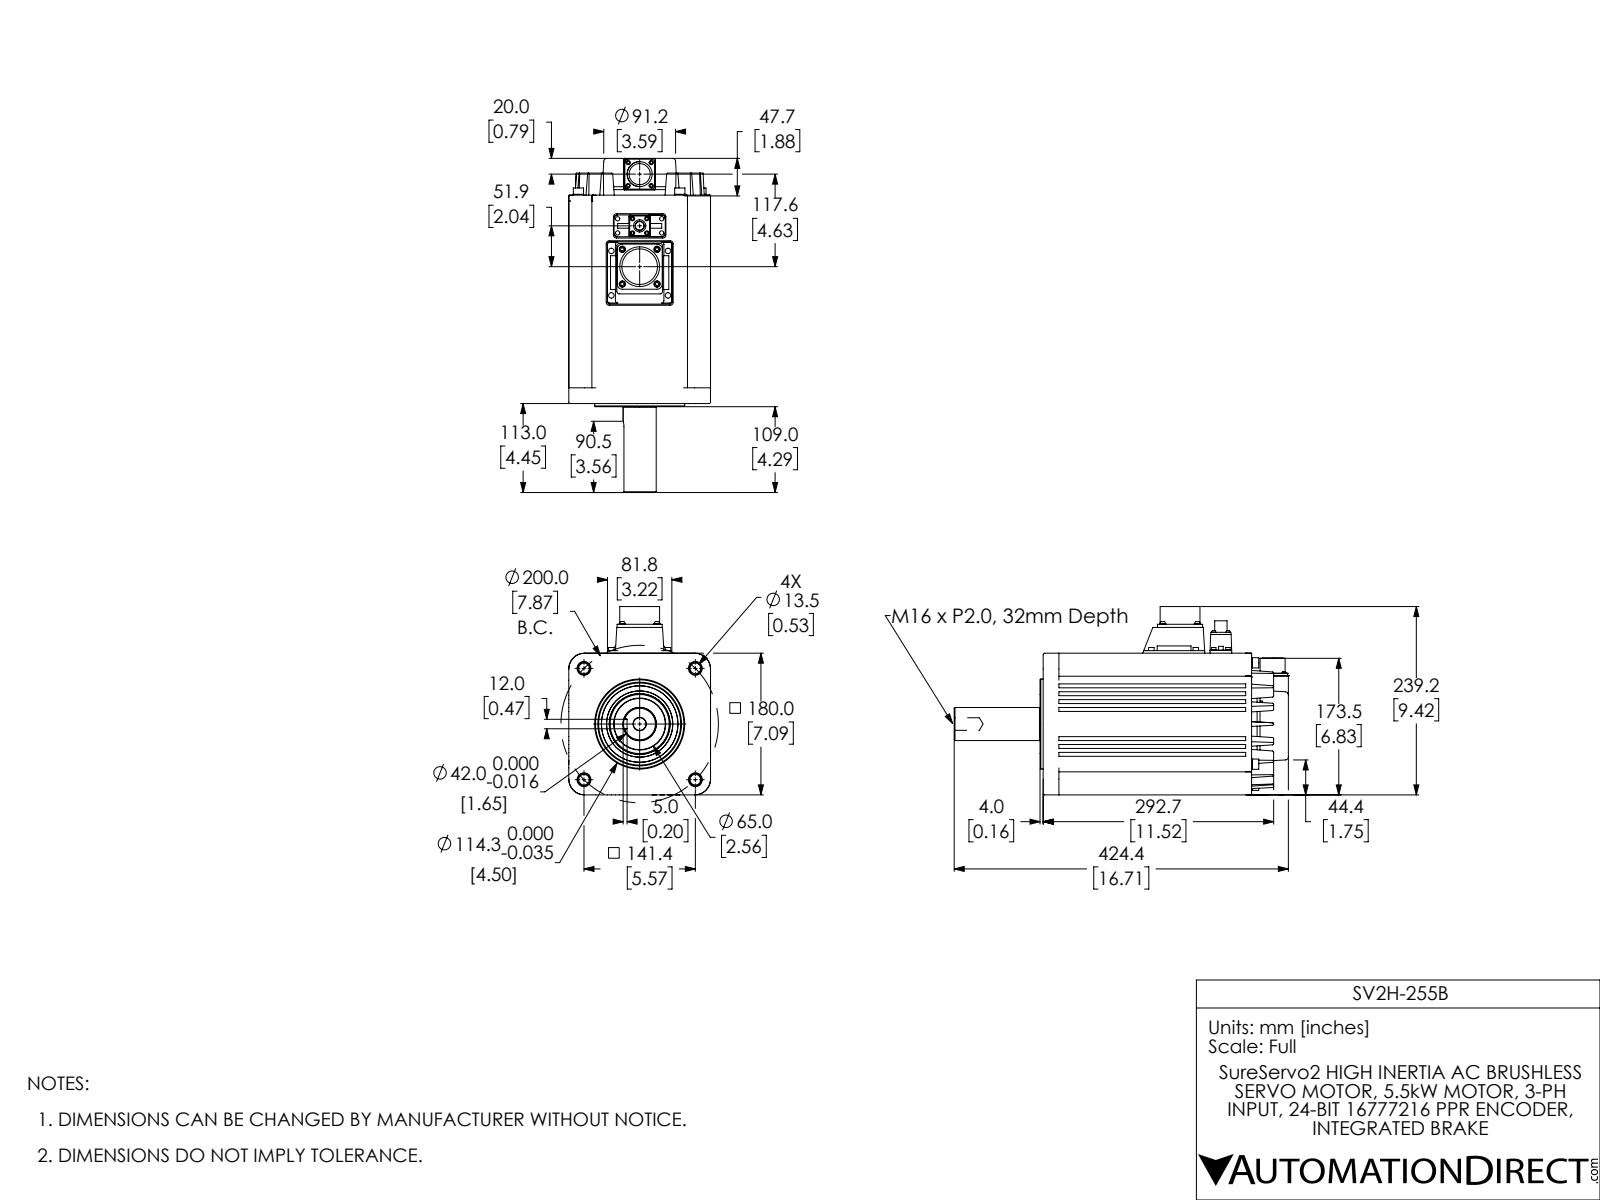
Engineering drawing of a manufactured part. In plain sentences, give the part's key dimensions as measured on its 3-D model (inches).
The part is named "SV2H-255B". Its 3-D file was written by "SolidWorks 2017 (AUTOMOTIVE_DESIGN)". It is 1 solid with 661 faces: 339 planar, 217 cylindrical and 105 other. Overall it measures 16.709 by 9.417 by 7.087 inches. Its volume is 509.7 cubic inches and its surface area 623.5 square inches. Round holes: 2 of diameter 0.315, 1 of diameter 0.461, 1 of diameter 0.63, 1 of diameter 1.058, 1 of diameter 1.783, 1 of diameter 2.559. Round bosses or shafts: 7 of diameter 0.217, 4 of diameter 0.528, 4 of diameter 0.512, 4 of diameter 0.315, 4 of diameter 0.276, 4 of diameter 0.236, 1 of diameter 4.567, 1 of diameter 4.5. Partial cylindrical surfaces (rounded edges, fillets, slot ends): 16 of radius 0.064, 16 of radius 0.197, 12 of radius 0.039, 12 of radius 0.118, 8 of radius 0.02, 8 of radius 0.079, 8 of radius 0.15, 8 of radius 0.157. The main face-to-face distances are 0.197, 0.394, 7.087, 1.154, 5.933, 0.591, 3.031, 3.228, 2.835, 0.787. The hole center spacings are 3.661, 2.041, 2.587, 4.628, 7.323.
